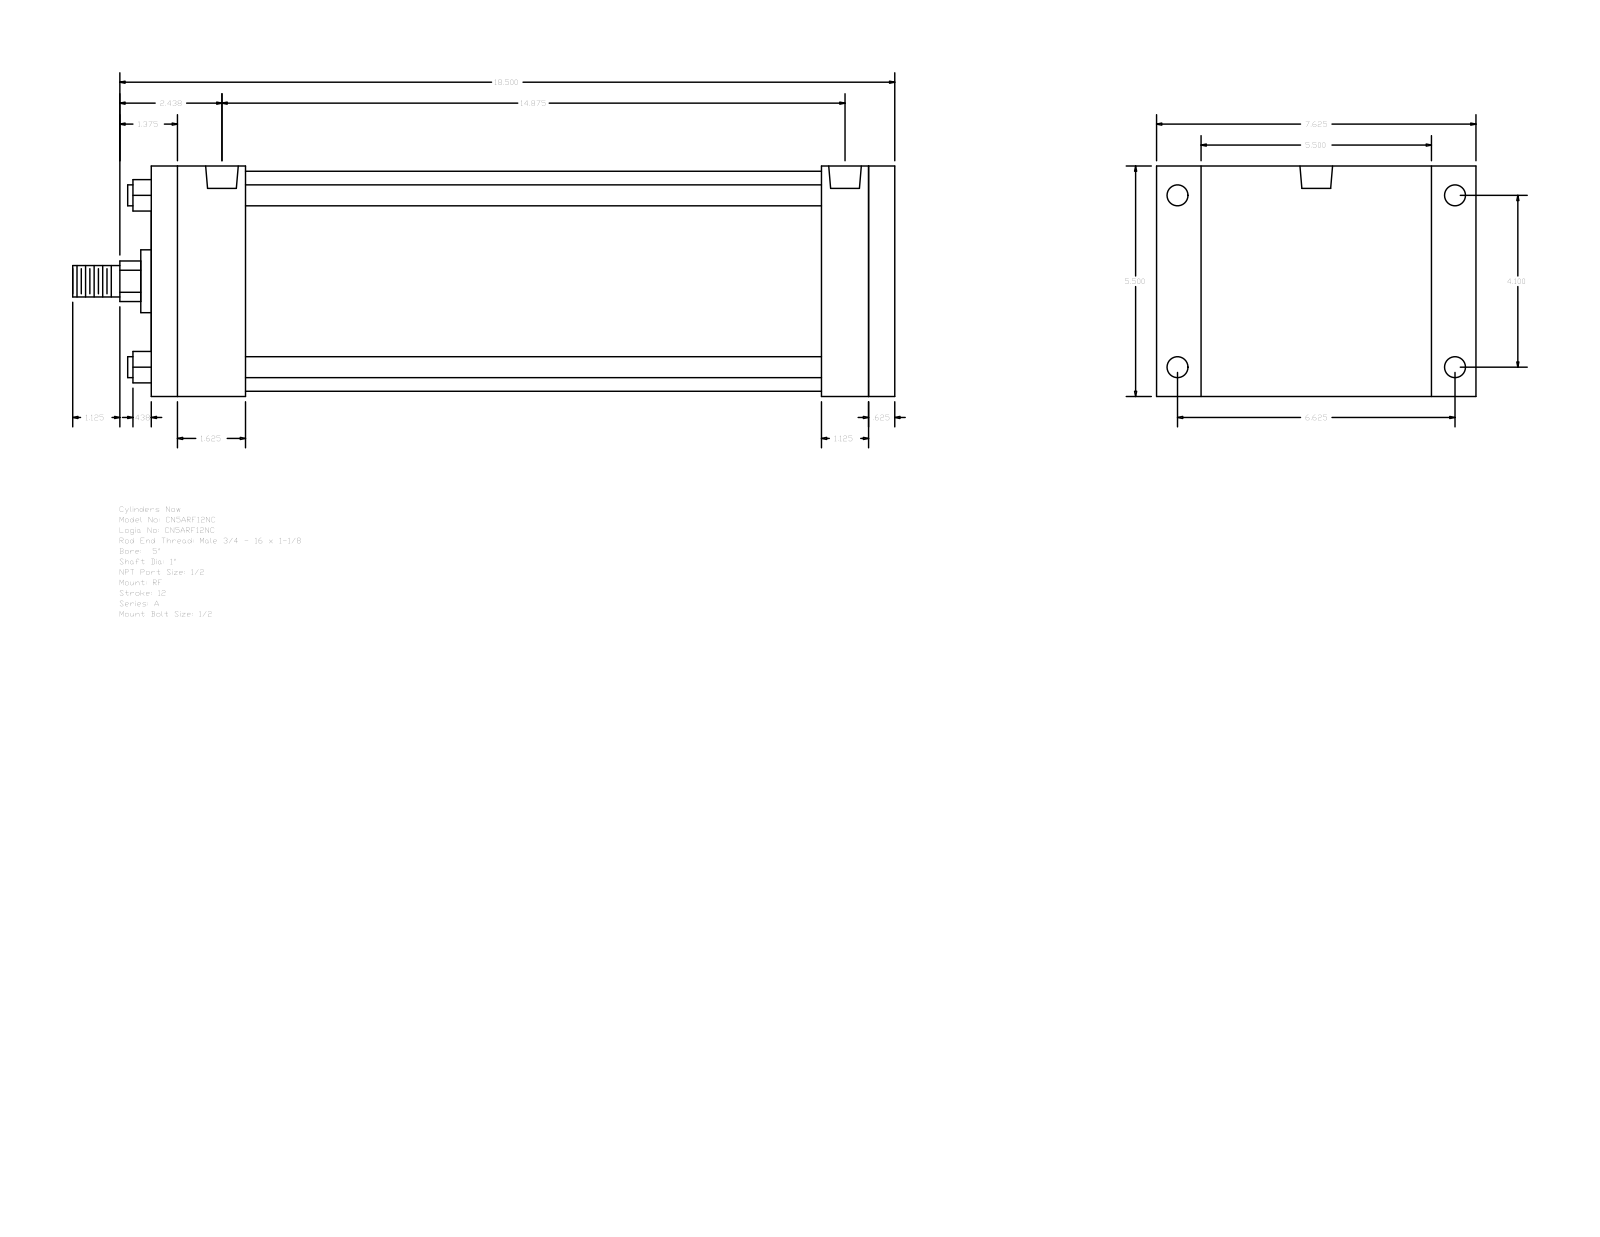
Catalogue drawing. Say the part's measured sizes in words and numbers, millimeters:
The part is named "A_RF__0500_1". Its 3-D file was written by "GSSL Pune (CONFIG_CONTROL_DESIGN)". It is 0 solids with 92 faces: 64 planar, 28 cylindrical and 0 other. Overall it measures 498.48 by 193.68 by 139.7 millimeters. Round holes: 4 of diameter 8.73, 4 of diameter 12.7, 2 of diameter 19.77. Round bosses or shafts: 4 of diameter 12.7, 1 of diameter 133.35, 1 of diameter 38.1, 1 of diameter 25.4, 1 of diameter 19.05. Partial cylindrical surfaces (rounded edges, fillets, slot ends): 1 of radius 12.29. The main face-to-face distances are 139.7, 450.85, 434.97, 15.88, 28.57, 57.15, 377.82, 393.7, 406.4, 349.25. The hole center spacings are 2.39, 104.14, 168.28, 197.9, 373.05, 375.44, 377.83.
